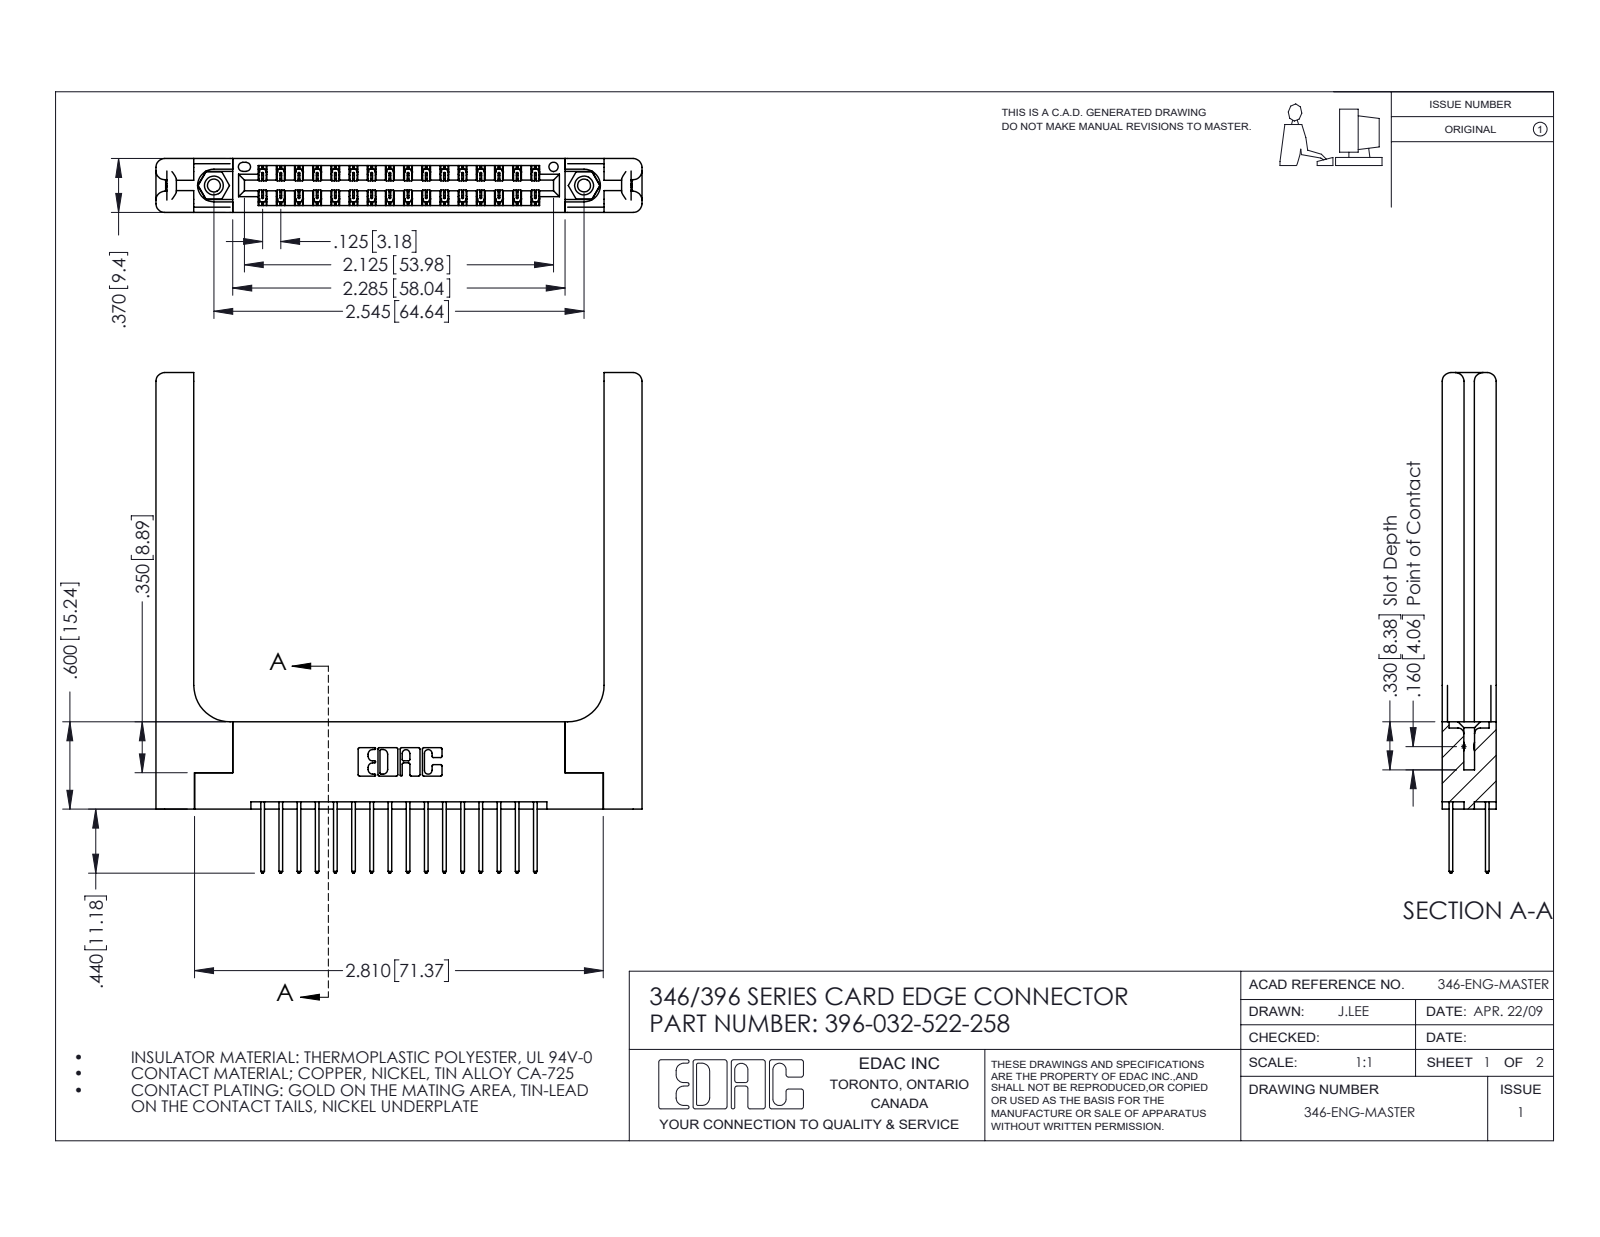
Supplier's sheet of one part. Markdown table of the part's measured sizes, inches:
| quantity | value |
| --- | --- |
| part name | 346-220-058_345-220-058; 345-292-001_345-293-122; 346 Part_Flush Mounting Lugs - 0.156 Dia-TH; 345-250-001_345-250-001-102 (+1 more) |
| STEP written by | SolidWorks 2016 (CONFIG_CONTROL_DESIGN) |
| units | inches |
| bodies | 37 solids, 2042 faces (1344 planar, 638 cylindrical, 60 other) |
| overall size | 3.44 × 3.341 × 0.37 |
| volume | 0.955 in³ |
| surface area | 25.04 in² |
| round holes (diameter × count) | 0.089 × 2, 0.125 × 2, 0.156 × 2, 0.064 × 1 |
| round bosses / shafts (diameter × count) | 0.155 × 2 |
| partial cylindrical surfaces (radius × count) | 0.006 × 48, 0.01 × 32, 0.01 × 22, 0.06 × 16, 0.007 × 6, 0.031 × 6, 0.026 × 3, 0.014 × 2 |
| main face-to-face distances | 0.37, 0.072, 0.048, 0.322, 0.148, 0.15, 0.25, 0.025, 0.298, 0.077 |
| hole center spacings | 0.246, 2.338, 2.545 |
